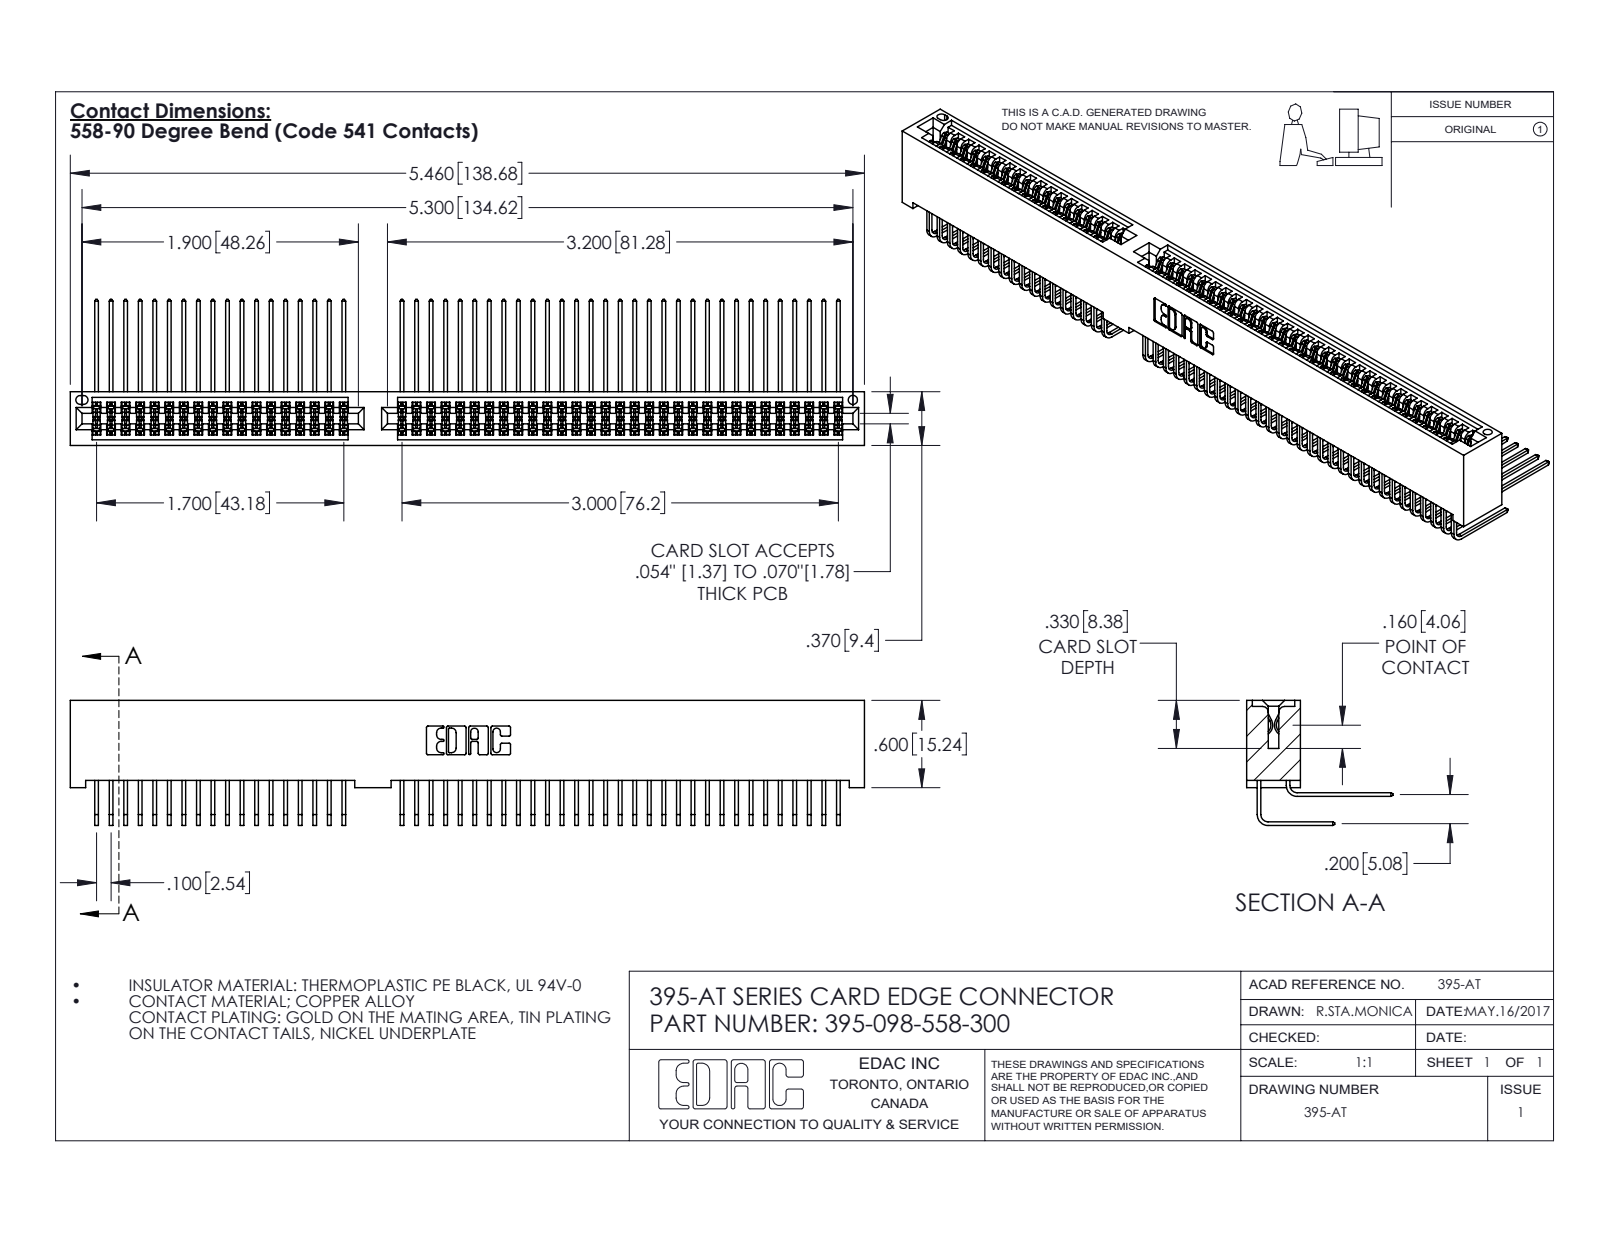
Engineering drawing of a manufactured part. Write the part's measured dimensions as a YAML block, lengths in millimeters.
part_name: "345-292-001_558 559 Tail - 1; 345-292-001_558 Tail - 2; 395-AT Part_No Mounting Lugs; 395-098-558-300"
step_written_by: "SolidWorks 2020 (AUTOMOTIVE_DESIGN)"
units: millimeters
bodies: {solids: 99, faces: 5227, planar: 3521, cylindrical: 1706, other: 0}
overall_size: [138.7, 25.5, 21.8]
volume: 14700
surface_area: 23920
round_holes:
  - {diameter: 1.6, count: 1}
partial_cylinders:
  - {radius: 0.2, count: 148}
  - {radius: 0.3, count: 22}
  - {radius: 0.2, count: 6}
  - {radius: 0.8, count: 6}
  - {radius: 0.7, count: 3}
  - {radius: 0.4, count: 2}
  - {radius: 0.5, count: 2}
  - {radius: 0.6, count: 2}
face_to_face_distances: [1.8, 7.6, 5.1, 9.4, 2.5, 6.9, 0.6, 5.7, 0.6, 4.4]
